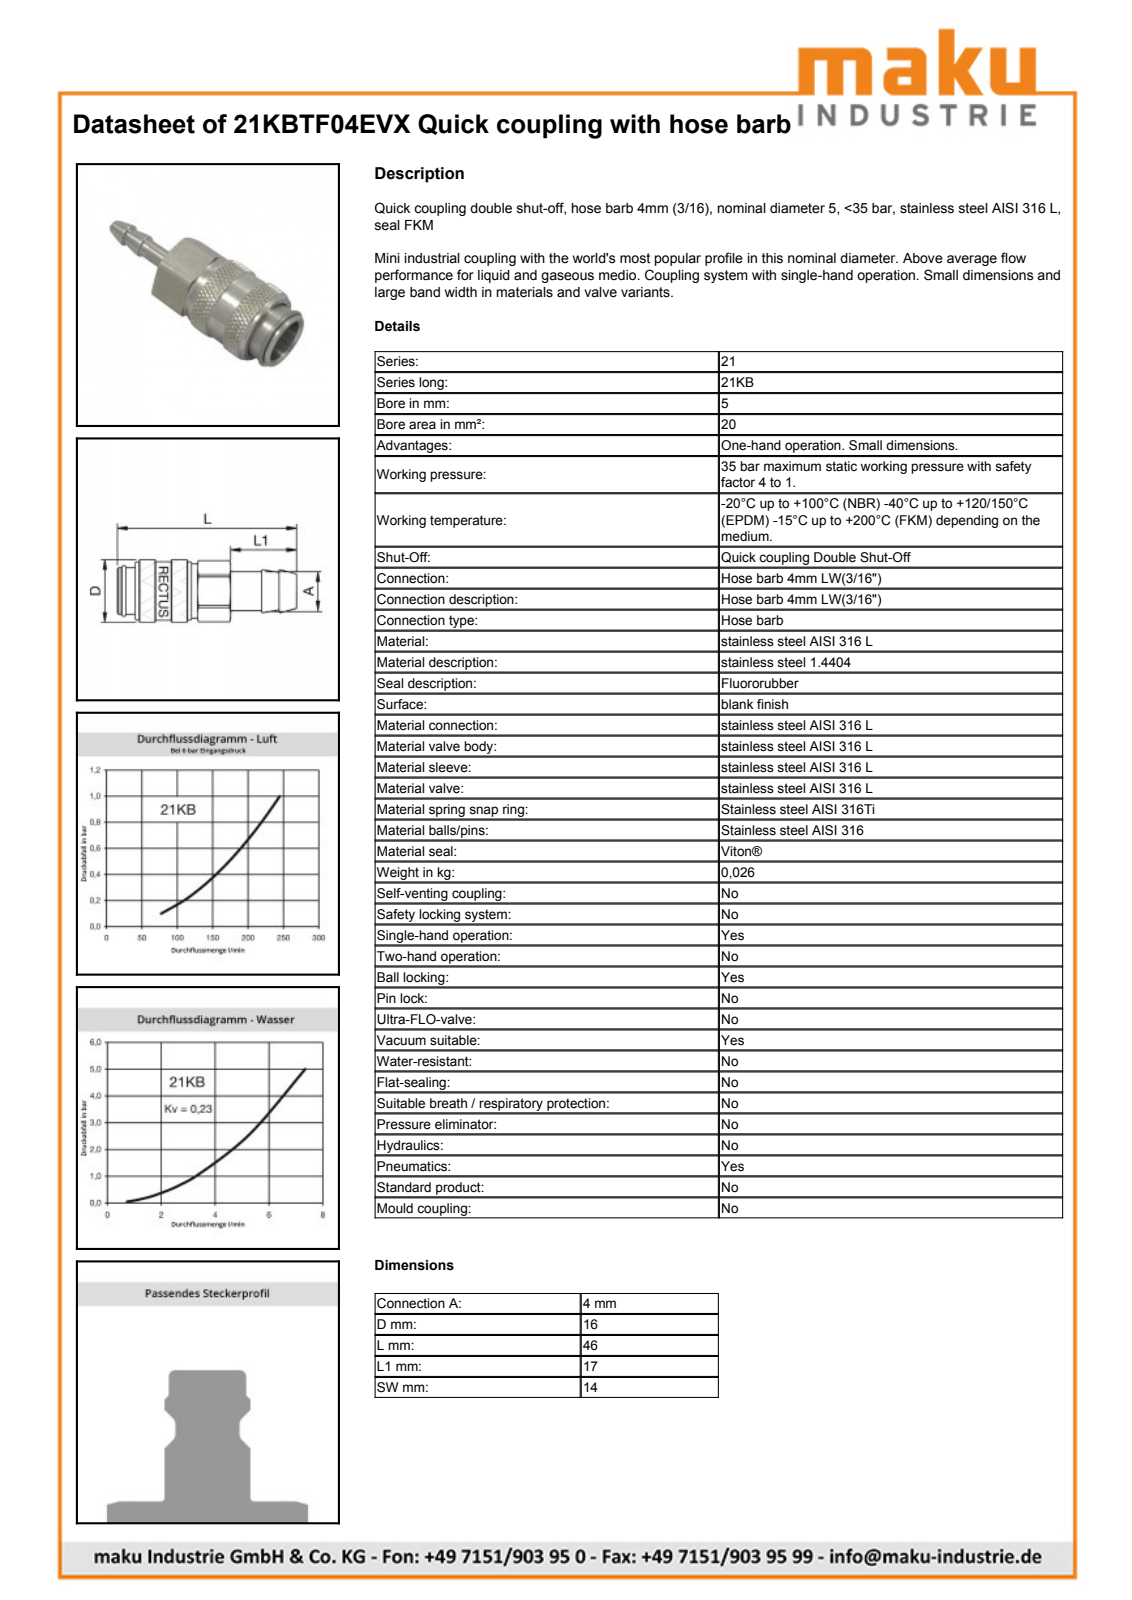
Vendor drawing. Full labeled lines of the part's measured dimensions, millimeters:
Part name (STEP PRODUCT): D105804
STEP written by: Autodesk Inventor 2011 (AUTOMOTIVE_DESIGN)
Units: millimetres
Bodies: 2 solids, 402 faces (164 planar, 63 cylindrical, 175 other)
Overall size (bounding box): 46.15 × 16.15 × 16.15
Volume: 4 917 mm³ · Surface area: 3 397 mm²
Round holes (diameter × count): ⌀12.15 ×1, ⌀14 ×1
Round bosses / shafts (diameter × count): ⌀16.15 ×1, ⌀15.1 ×1, ⌀12 ×1, ⌀11.4 ×1, ⌀11.15 ×1, ⌀4.05 ×1
Partial cylindrical surfaces — rounded edges, fillets, slot ends (radius × count): R5.5 ×1, R7.45 ×1, R7.9 ×1
Main face-to-face distances: 14, 29.15, 11.55, 16.15, 13, 4.6, 24.55, 11.9, 7.3, 4.25
